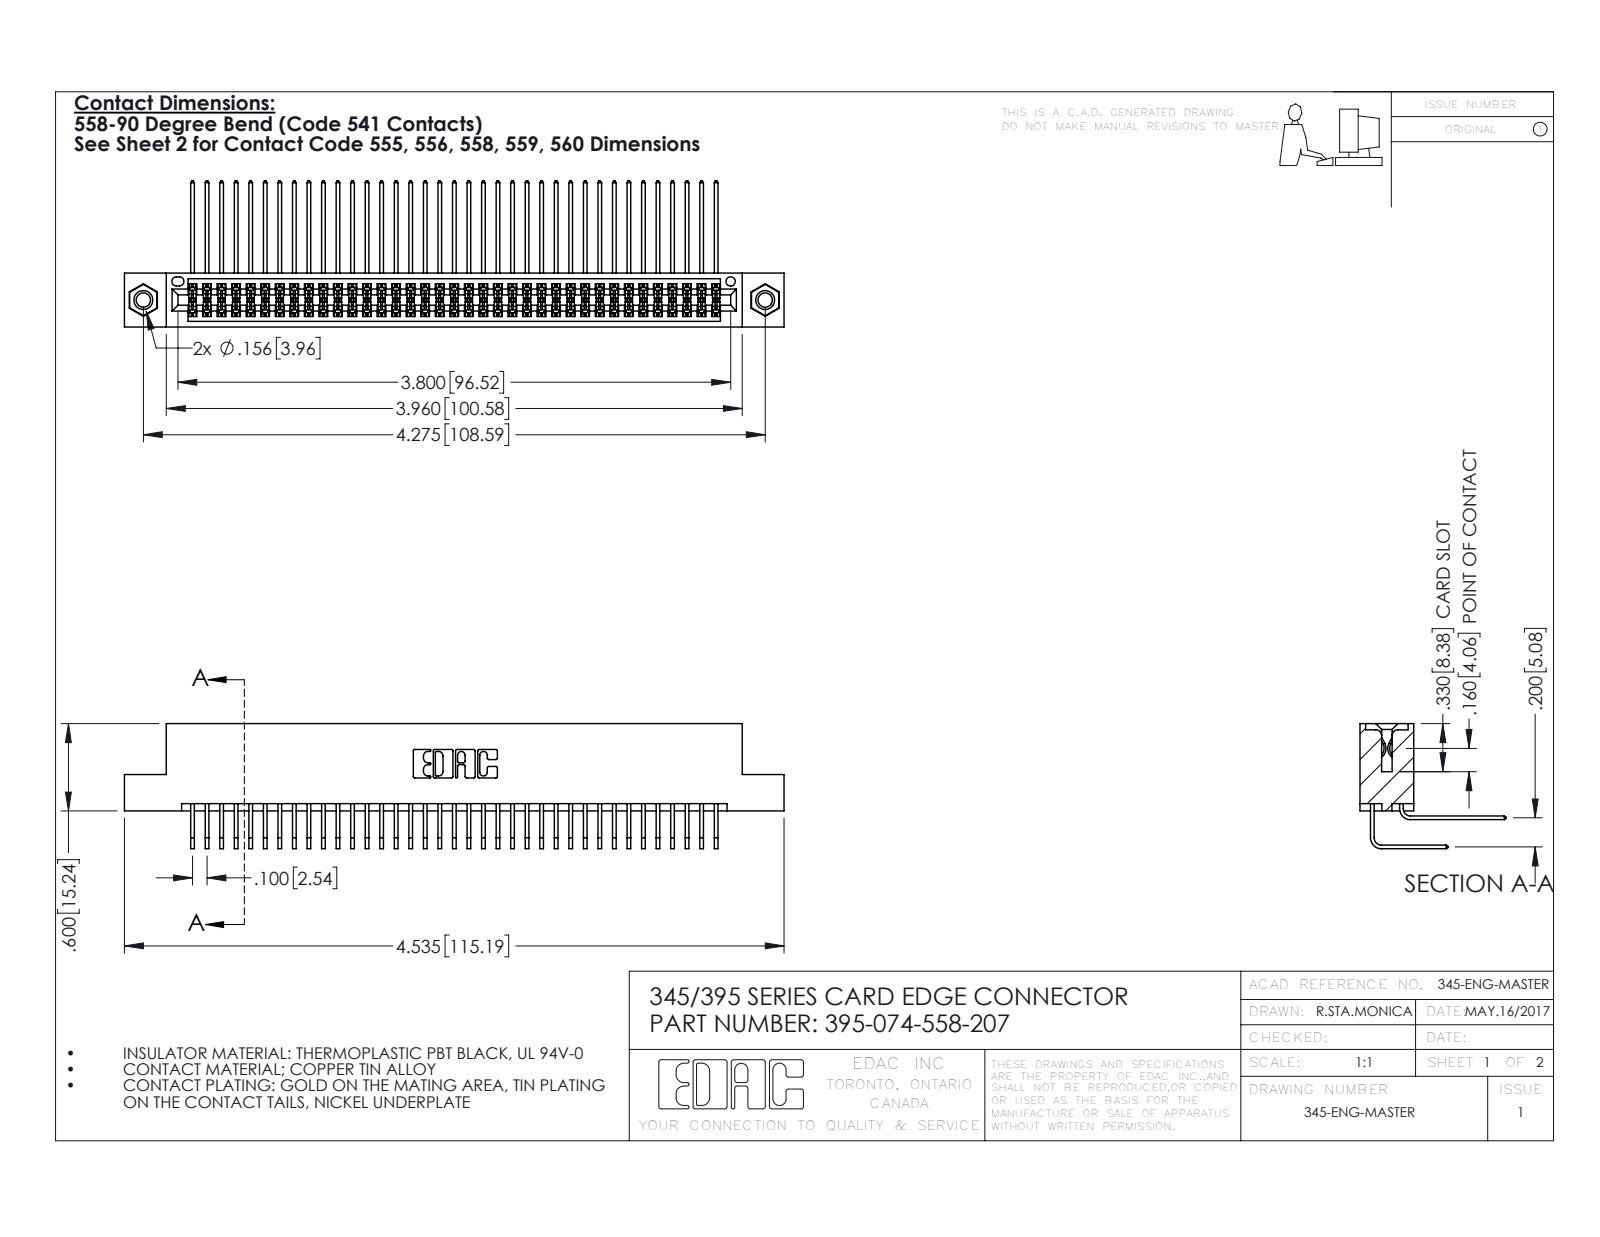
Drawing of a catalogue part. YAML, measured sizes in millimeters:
part_name: "345 Part_Flush Mounting Lugs - 0.156 Dia-TI; 345-292-001_558 Tail - 2; 345-292-001_558 559 Tail - 1; 395-074-558-207 (+1 more)"
step_written_by: "SolidWorks 2016 (CONFIG_CONTROL_DESIGN)"
units: millimeters
bodies: {solids: 77, faces: 4034, planar: 2702, cylindrical: 1316, other: 16}
overall_size: [115.2, 25.5, 21.8]
volume: 11600
surface_area: 19020
round_holes:
  - {diameter: 2.5, count: 2}
  - {diameter: 3.2, count: 2}
  - {diameter: 4, count: 2}
  - {diameter: 1.6, count: 1}
round_bosses_or_shafts:
  - {diameter: 3.9, count: 2}
partial_cylinders:
  - {radius: 0.2, count: 112}
  - {radius: 0.3, count: 22}
  - {radius: 0.2, count: 6}
  - {radius: 0.8, count: 6}
  - {radius: 0.7, count: 3}
  - {radius: 0.4, count: 2}
  - {radius: 0.5, count: 2}
  - {radius: 0.6, count: 2}
face_to_face_distances: [1.8, 7.6, 5.1, 9.4, 2.5, 6.9, 0.6, 5.7, 0.6, 4.4]
hole_center_spacings: [6.9, 102.6, 108.6]
